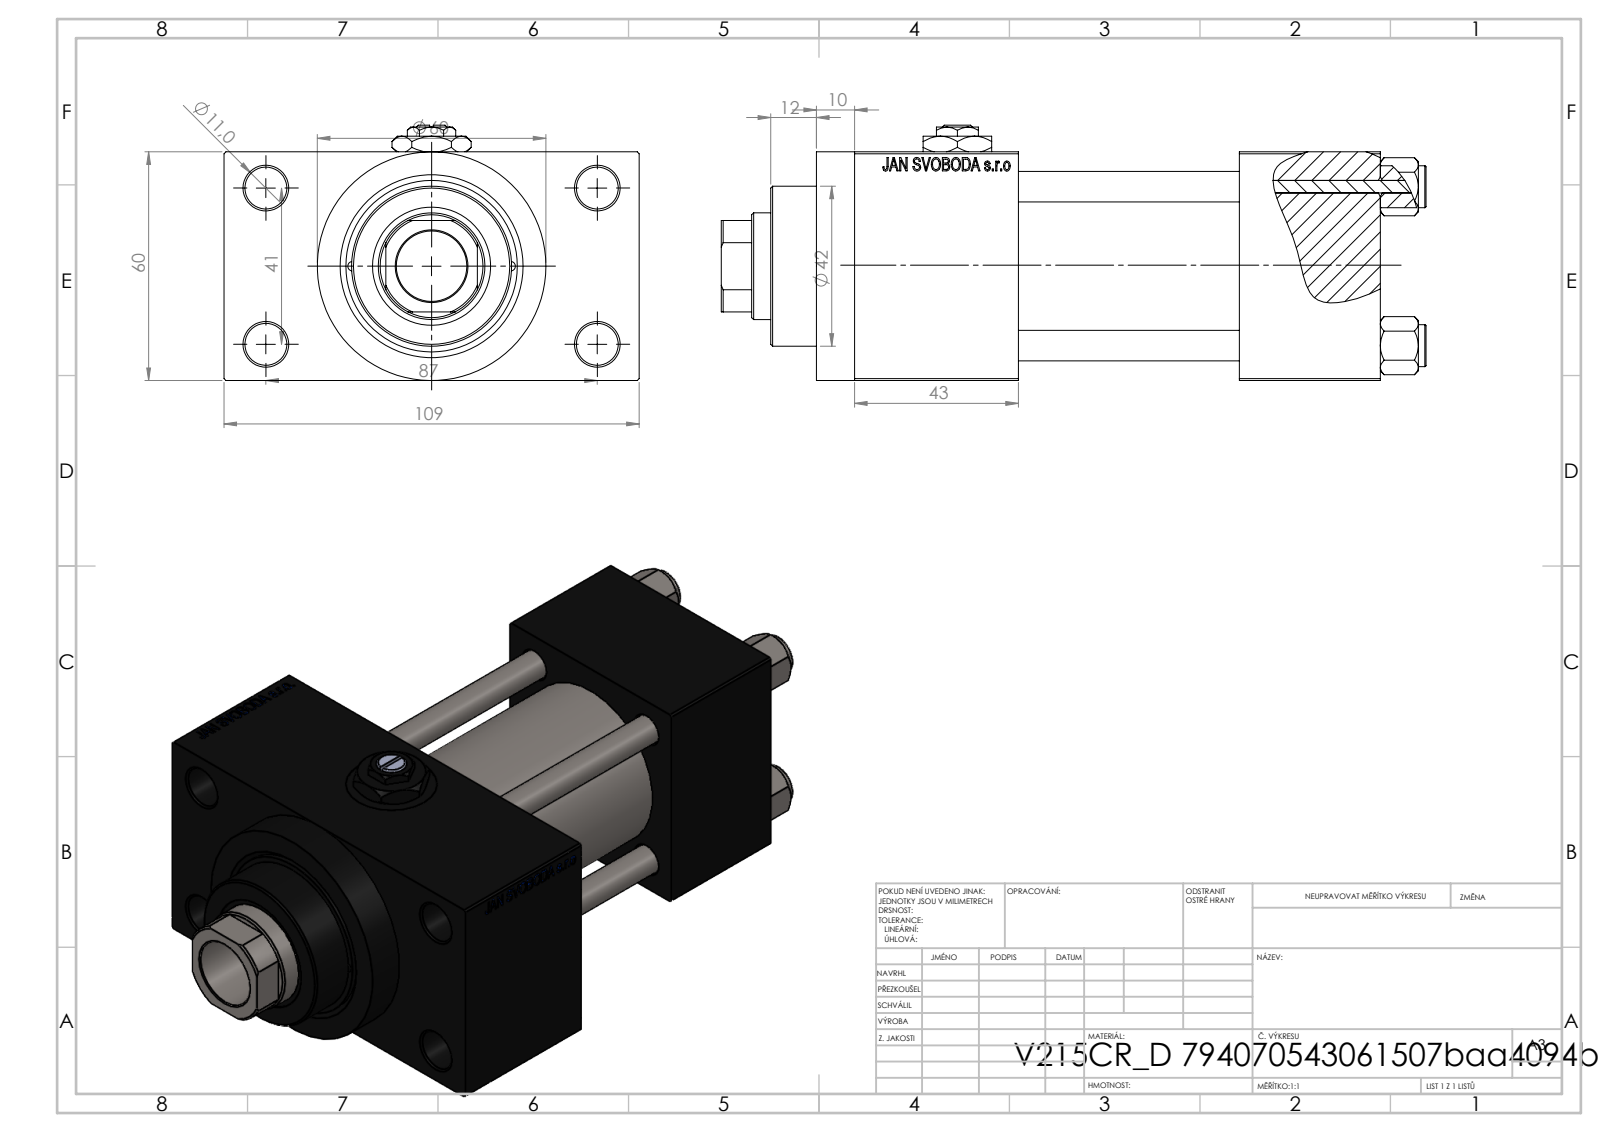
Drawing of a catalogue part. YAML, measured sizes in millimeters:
part_name: "NUT_M5_D; V215CR_D_TYCINKA; V215CR_VCP_D; Zatka_pro_OIL_PORT (+2 more)"
step_written_by: "SolidWorks 2019 (CONFIG_CONTROL_DESIGN)"
units: millimeters
bodies: {solids: 11, faces: 1160, planar: 524, cylindrical: 96, other: 540}
overall_size: [185, 109, 67]
volume: 430806
surface_area: 129790
round_holes:
  - {diameter: 8, count: 4}
  - {diameter: 11, count: 4}
  - {diameter: 16.66, count: 3}
  - {diameter: 24, count: 3}
  - {diameter: 2.5, count: 2}
  - {diameter: 7, count: 2}
  - {diameter: 18.5, count: 1}
  - {diameter: 28, count: 1}
  - {diameter: 31, count: 1}
  - {diameter: 40, count: 1}
  - {diameter: 45, count: 1}
round_bosses_or_shafts:
  - {diameter: 11, count: 4}
  - {diameter: 60, count: 1}
  - {diameter: 46, count: 1}
  - {diameter: 42, count: 1}
partial_cylinders:
  - {radius: 13.5, count: 1}
face_to_face_distances: [60, 58, 24.5, 84.5, 37, 95, 138, 101, 43, 109]
hole_center_spacings: [20.85, 22.65, 29.49, 30.62, 41.7, 46.53, 47.15, 48.09]
